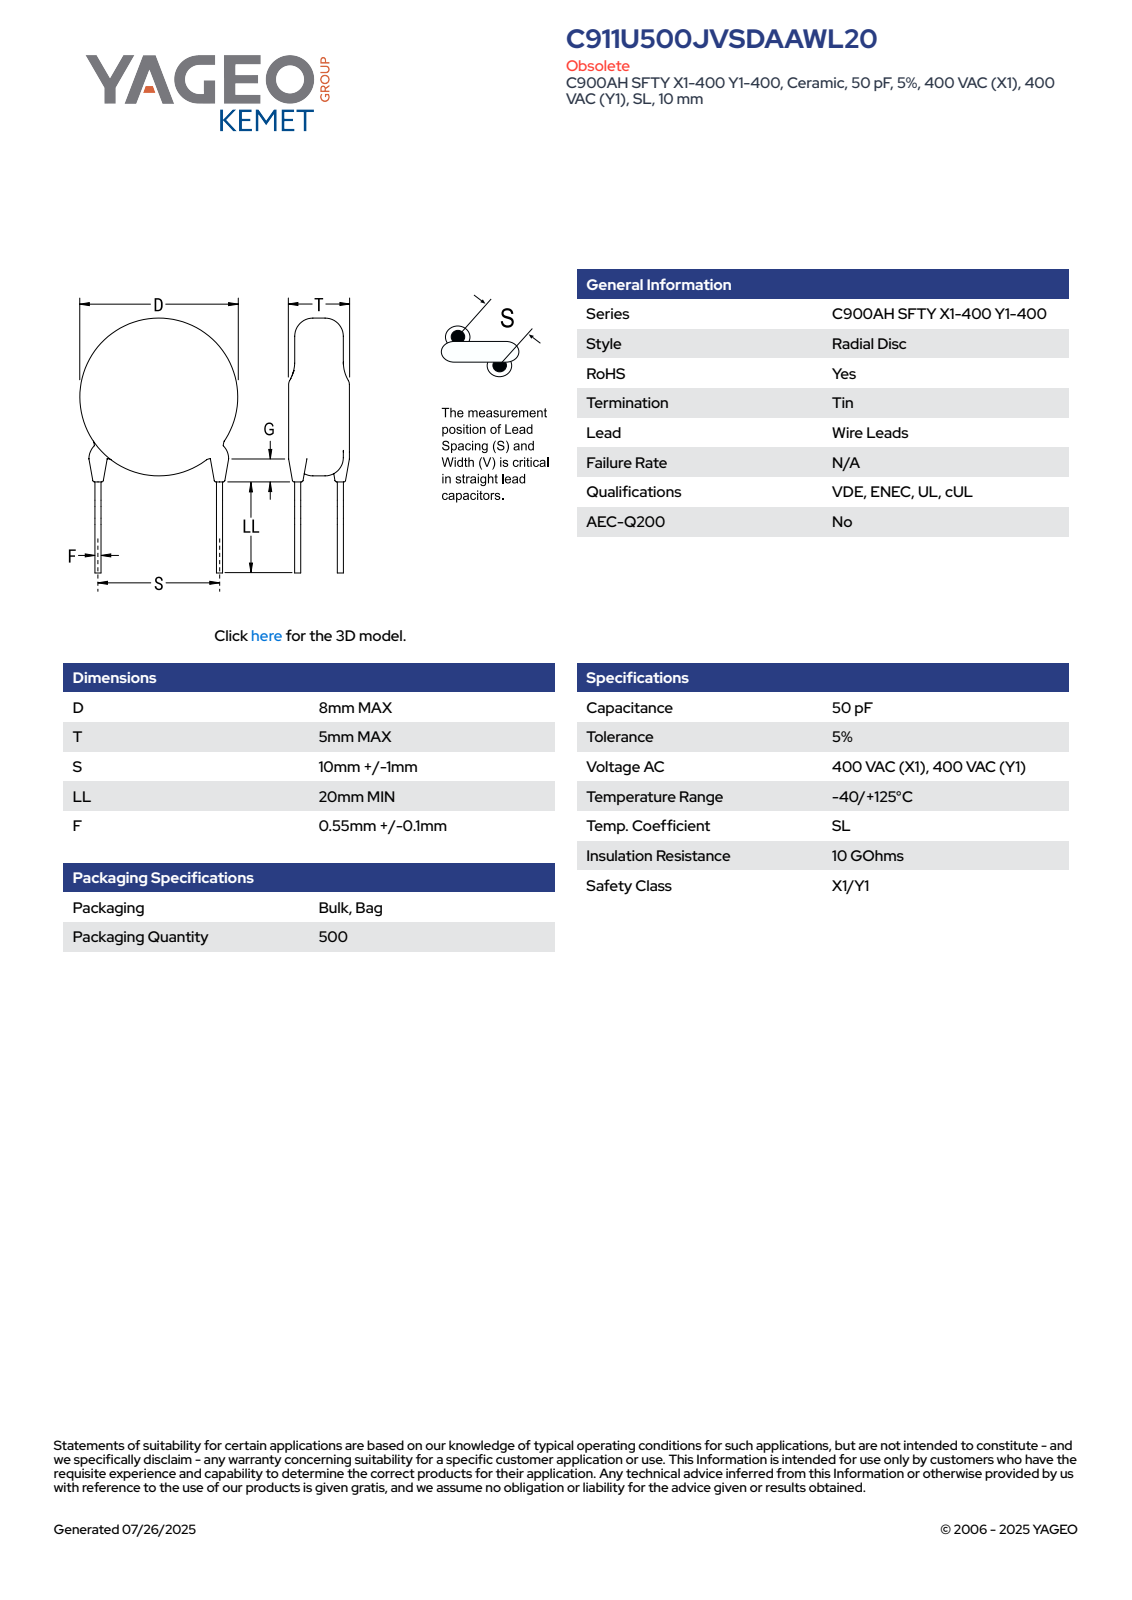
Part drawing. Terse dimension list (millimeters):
name: CCD_STC900_D8T5S10LL20F0.65G3
written by: SolidWorks 2014 (AUTOMOTIVE_DESIGN)
unit: mm
bodies: 4 solids, 83 faces (61 planar, 6 cylindrical, 16 other)
size: 28.42 × 10.19 × 5
volume: 259 mm³; area: 306 mm²
bosses: 2× ⌀0.65, 1× ⌀8
face distances: 5, 24.88, 23.96, 0.92, 0.4, 1.04, 3.77, 0.57, 2.73, 2.84
